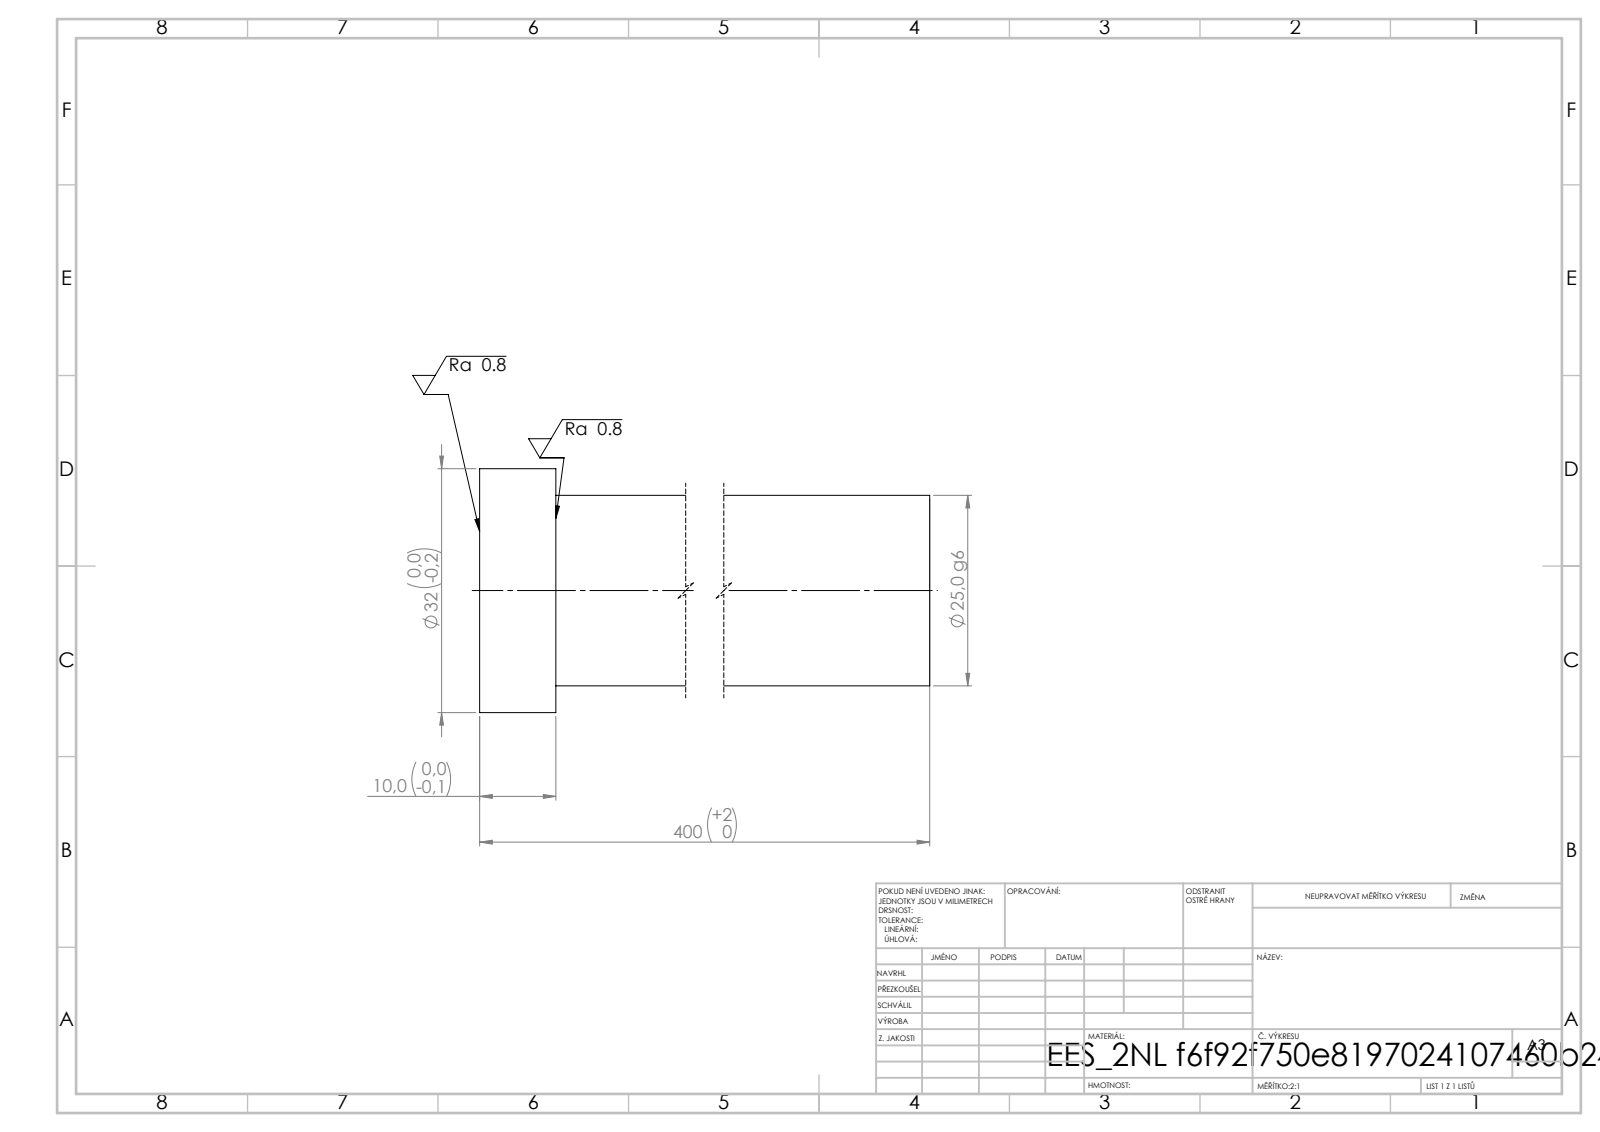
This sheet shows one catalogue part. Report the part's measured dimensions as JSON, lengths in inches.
{"step_written_by": "SolidWorks 2019 (CONFIG_CONTROL_DESIGN)", "units": "inches", "bodies": {"solids": 1, "faces": 7, "planar": 3, "cylindrical": 4, "other": 0}, "overall_size": [15.748, 1.26, 1.26], "volume_in3": 12.17, "surface_area_in2": 51.53, "round_bosses_or_shafts": [[1.26, 1], [0.984, 1]], "face_to_face_distances": [15.748, 0.394, 15.354]}
